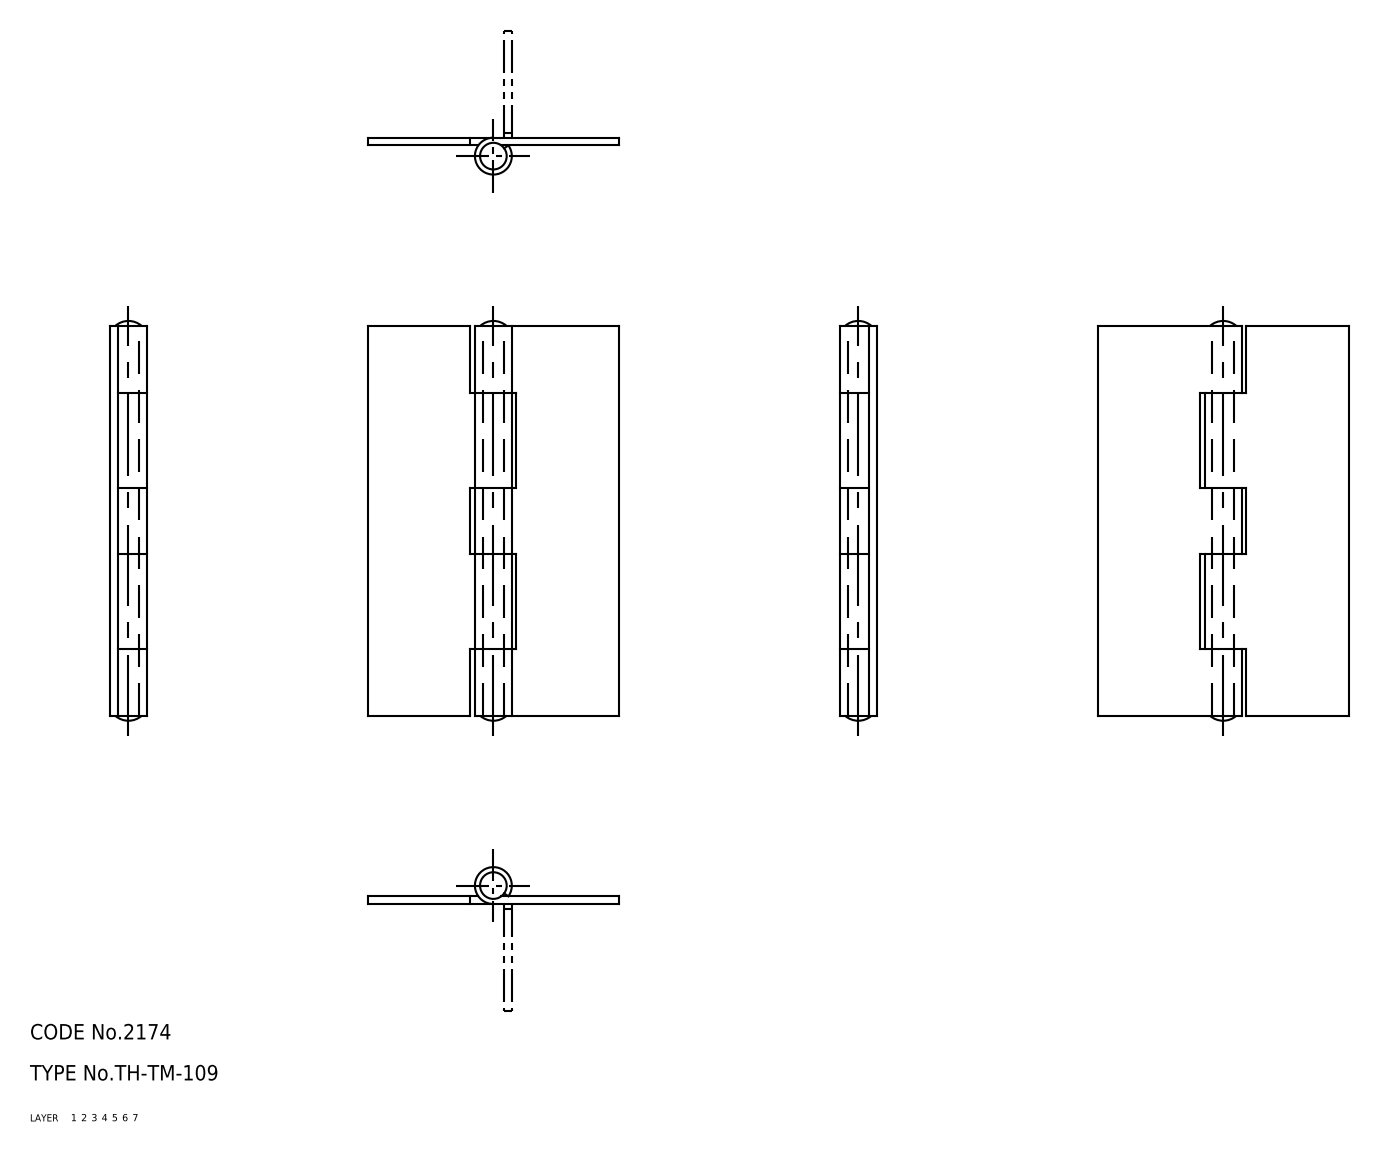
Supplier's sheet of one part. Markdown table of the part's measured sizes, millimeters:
| quantity | value |
| --- | --- |
| part name | 67111025; 67111038; 67111051 |
| STEP written by | CADfix (AUTOMOTIVE_DESIGN) |
| units | millimeters |
| bodies | 3 solids, 44 faces (0 planar, 0 cylindrical, 44 other) |
| overall size | 78 × 49 × 7.2 |
| volume | 7 878 mm³ |
| surface area | 11 006 mm² |
